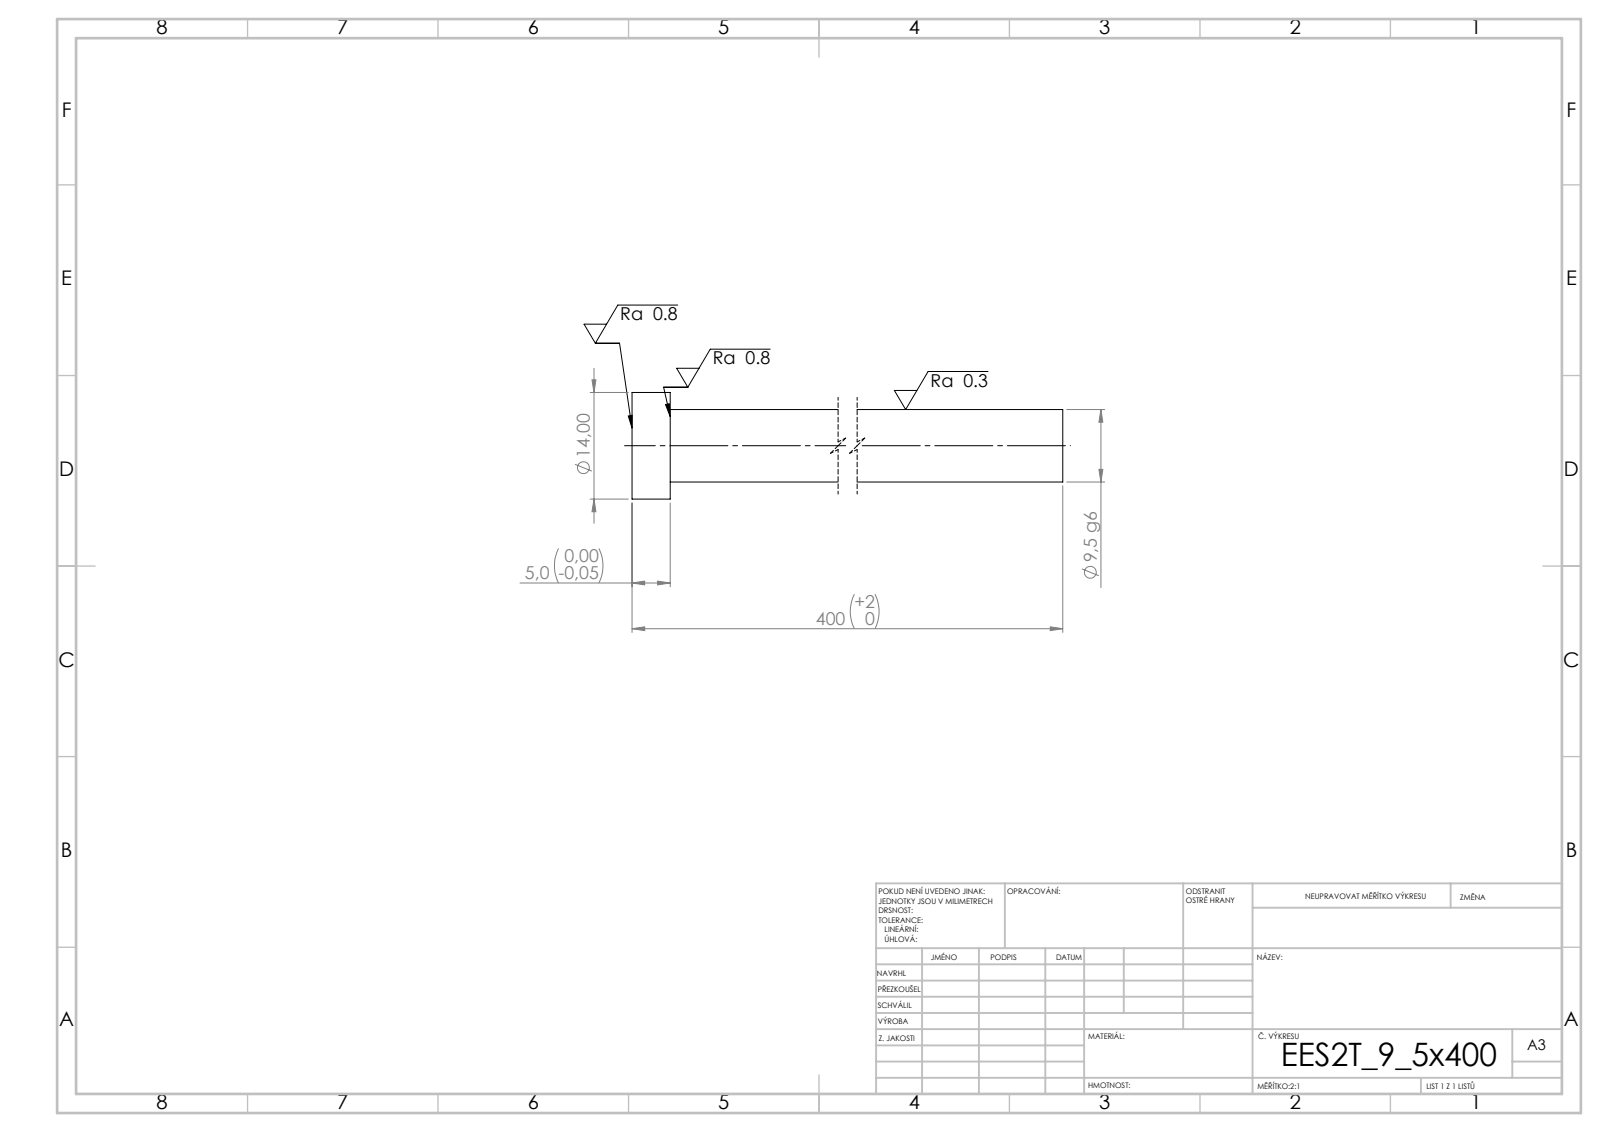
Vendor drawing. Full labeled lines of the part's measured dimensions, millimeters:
STEP written by: SolidWorks 2019 (CONFIG_CONTROL_DESIGN)
Units: millimetres
Bodies: 1 solid, 7 faces (3 planar, 4 cylindrical, 0 other)
Overall size (bounding box): 400 × 14 × 14
Volume: 28 768 mm³ · Surface area: 12 317 mm²
Round bosses / shafts (diameter × count): ⌀14 ×1, ⌀9.5 ×1
Main face-to-face distances: 5, 400, 395
